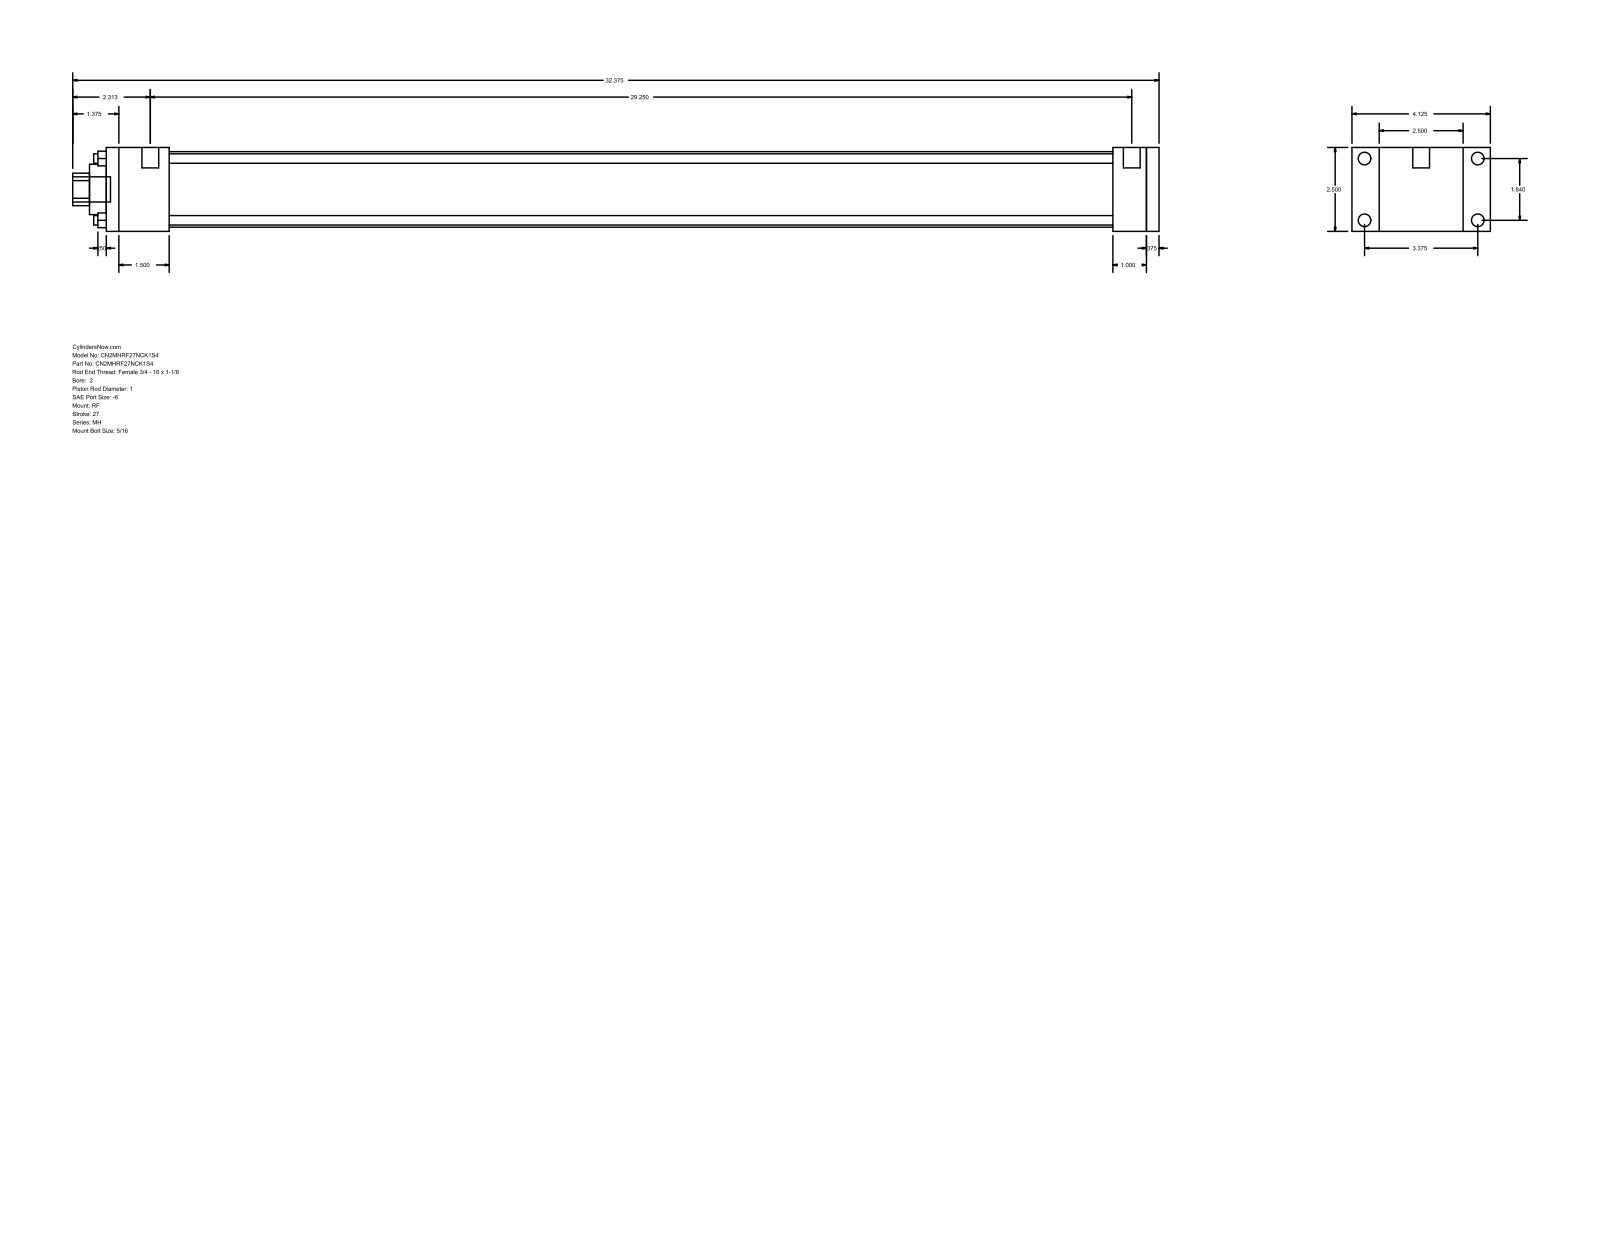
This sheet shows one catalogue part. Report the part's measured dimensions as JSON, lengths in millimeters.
{"part_name": "MH_RF__0200_1", "step_written_by": "GSSL Pune (CONFIG_CONTROL_DESIGN)", "units": "millimeters", "bodies": {"solids": 0, "faces": 92, "planar": 64, "cylindrical": 28, "other": 0}, "overall_size": [822.33, 104.78, 63.5], "round_holes": [[7.14, 4], [25.4, 1], [38.1, 1], [57.15, 1]], "round_bosses_or_shafts": [[9.53, 4], [5.56, 4], [12.7, 2], [19.05, 1]], "partial_cylinders_radius": [[12.29, 1]], "face_to_face_distances": [63.5, 796.93, 787.4, 9.53, 20.64, 25.4, 47.63, 762, 714.37, 739.77], "hole_center_spacings": [33.05, 46.74, 66.1]}
